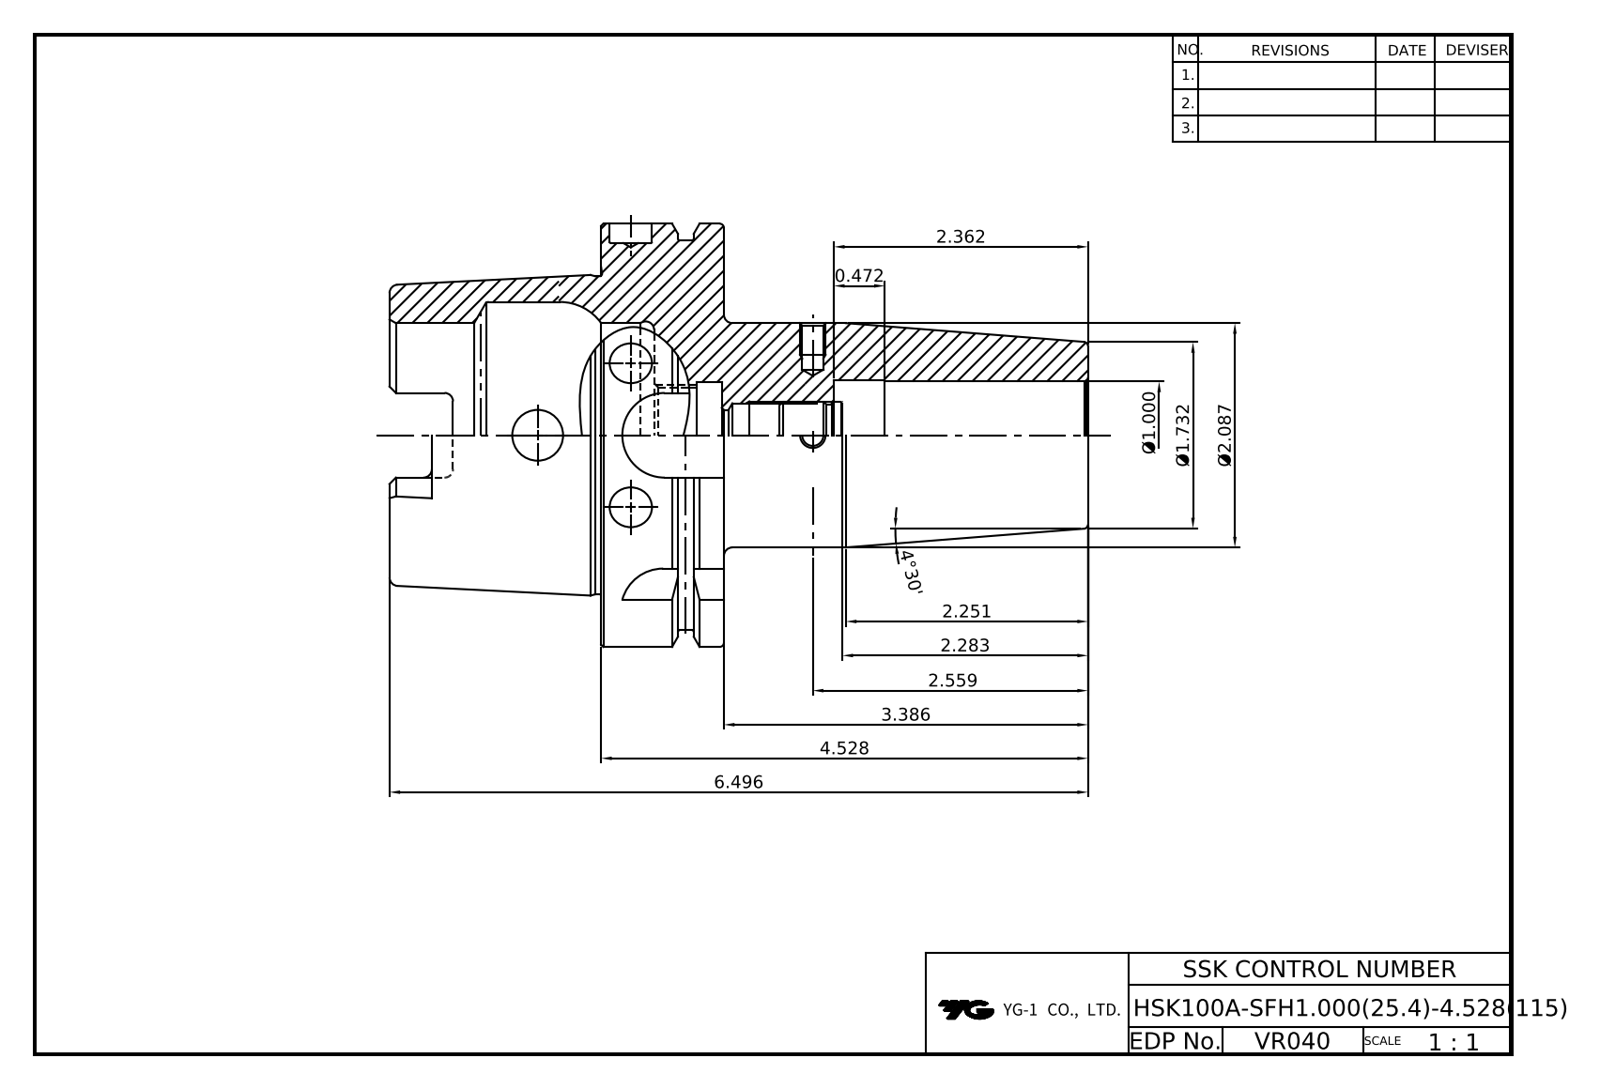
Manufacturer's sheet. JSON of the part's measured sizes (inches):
{"part_name": "HSK100A-SFH1-4_63", "step_written_by": "CREO PARAMETRIC BY PTC INC, 2018400 (CONFIG_CONTROL_DESIGN)", "units": "inches", "bodies": {"solids": 1, "faces": 212, "planar": 56, "cylindrical": 70, "other": 86}, "overall_size": [6.496, 3.937, 3.937], "volume_in3": 23.5, "surface_area_in2": 109.4, "round_holes": [[0.197, 2], [0.236, 2], [0.472, 2], [0.394, 1], [0.594, 1], [0.886, 1], [0.945, 1], [0.984, 1], [1, 1], [1.024, 1], [2.087, 1], [2.518, 1]], "round_bosses_or_shafts": [[3.937, 1], [3.622, 1], [2.959, 1]], "partial_cylinders_radius": [[0.079, 6], [0.192, 4], [0.394, 4]], "face_to_face_distances": [1.142, 0.492, 0.65, 2.461, 1.969, 3.11, 6.496, 4.528, 4.035, 3.386], "hole_center_spacings": [1.693, 2.559]}
